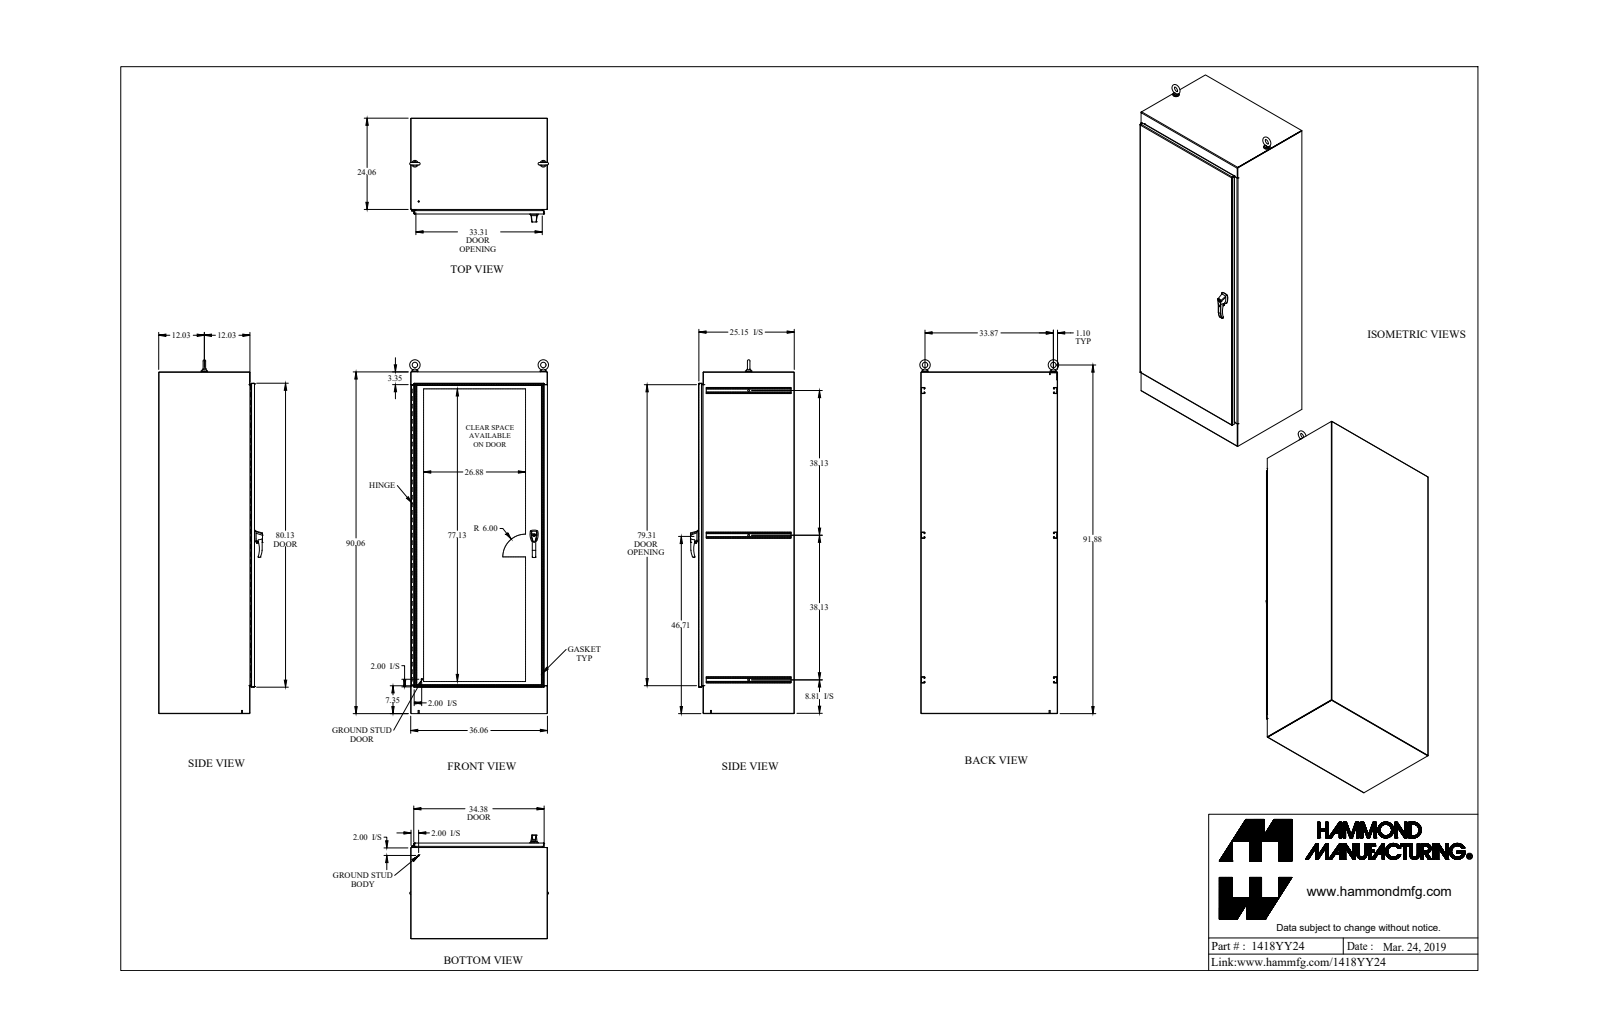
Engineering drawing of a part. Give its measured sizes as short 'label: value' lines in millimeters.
name: 1418YY24_Default
written by: SolidWorks 2019 (CONFIG_CONTROL_DESIGN)
unit: mm
bodies: 54 solids, 2636 faces (1132 planar, 1339 cylindrical, 165 other)
size: 2380.3 × 942.8 × 695
volume: 22 580 000 mm³; area: 18 810 000 mm²
holes: 14× ⌀7.7, 4× ⌀19.1, 3× ⌀12.7, 2× ⌀6.4, 2× ⌀6.5, 2× ⌀7.1, 2× ⌀7.1, 2× ⌀8, 2× ⌀9.9, 2× ⌀10.5, 2× ⌀13.4, 2× ⌀15.9
bosses: 4× ⌀7.1, 2× ⌀44.5, 2× ⌀38.1, 2× ⌀31.8, 2× ⌀25.4, 2× ⌀19.1, 2× ⌀18.7, 2× ⌀16
rounds: 42× R1.1, 36× R3.5, 22× R3.2, 16× R0.5, 12× R1.2, 12× R3.6, 10× R1.5, 7× R8.1
face distances: 2.4, 638.9, 913.5, 636.4, 641.3, 911.1, 915.9, 2285.1, 30.1, 608.7
hole spacings: 152.4, 304.8, 457.2, 609.6, 762, 914.4, 1066.8, 1219.2
